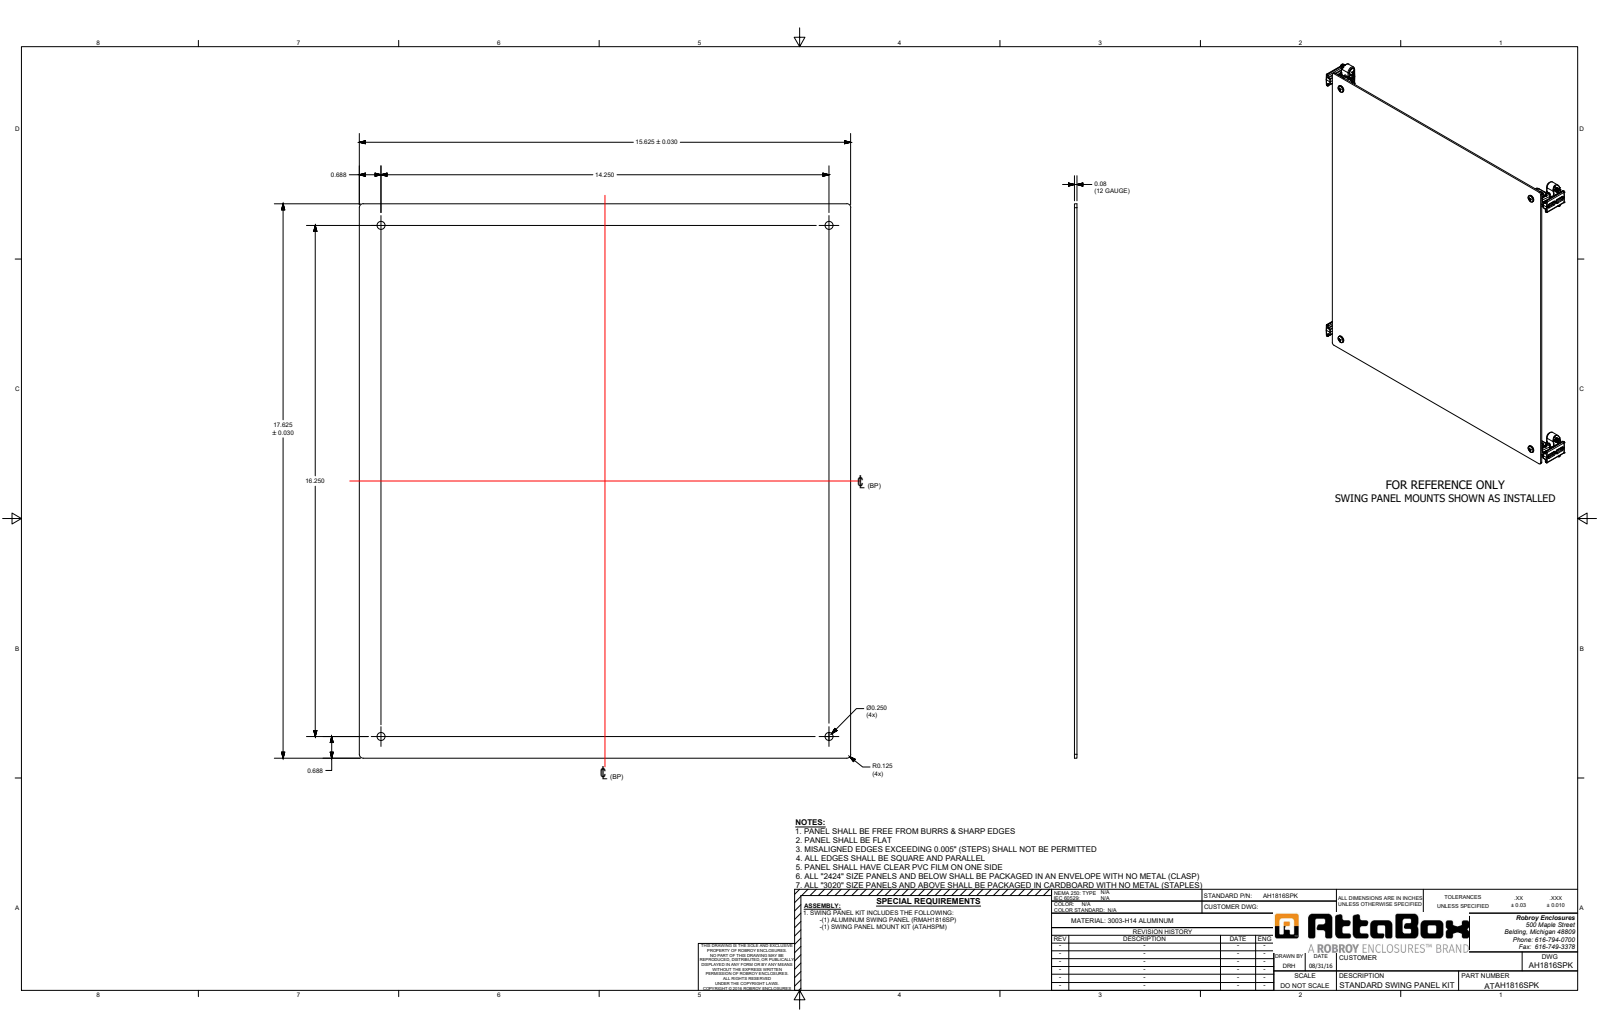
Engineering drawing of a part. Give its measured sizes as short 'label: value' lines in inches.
name: AH1816SPK
written by: SolidWorks 2019 (AUTOMOTIVE_DESIGN)
unit: in
bodies: 33 solids, 2010 faces (518 planar, 736 cylindrical, 756 other)
size: 17.625 × 16.559 × 1.448
volume: 25.1 in³; area: 613.4 in²
holes: 8× ⌀0.156, 8× ⌀0.25
bosses: 8× ⌀0.373, 8× ⌀0.262, 8× ⌀0.19
rounds: 248× R0.035, 124× R0.02, 54× R0.065, 30× R0.015, 16× R0.045, 16× R0.05, 10× R0.025, 8× R0.9
face distances: 0.08, 0.276, 16.25, 0.5, 0.276, 15.625, 17.625, 0.51, 0.59, 0.3
hole spacings: 16.25, 0.875, 14.25, 21.613, 15.375, 17.125
